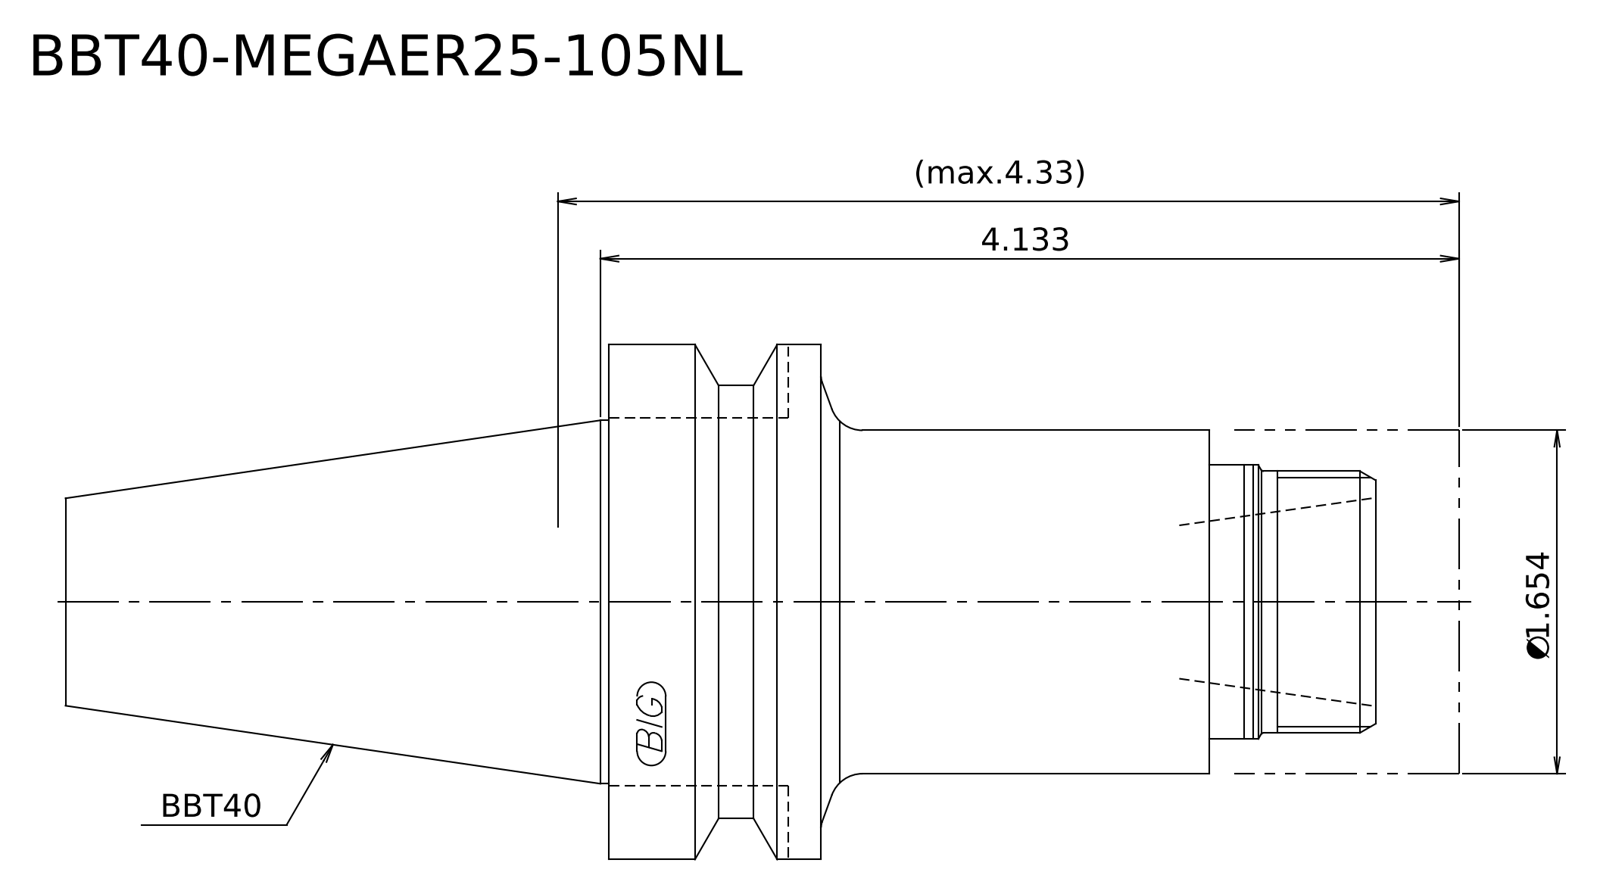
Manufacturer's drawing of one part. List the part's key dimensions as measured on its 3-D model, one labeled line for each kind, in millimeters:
STEP written by: Kubotek KeyCreator 2011 V10.0.2 (22737) (automotive_design)
Units: millimetres
Bodies: 2 solids, 21 faces (7 planar, 8 cylindrical, 6 other)
Overall size (bounding box): 170.4 × 63 × 63
Volume: 263 180 mm³ · Surface area: 32 764 mm²
Round bosses / shafts (diameter × count): ⌀63 ×1, ⌀53 ×1, ⌀44.45 ×1, ⌀42 ×1, ⌀33.5 ×1, ⌀32 ×1
Main face-to-face distances: 76.5, 27.5, 104, 78, 50.5, 26, 10.2, 17.3, 67.8, 93.8
